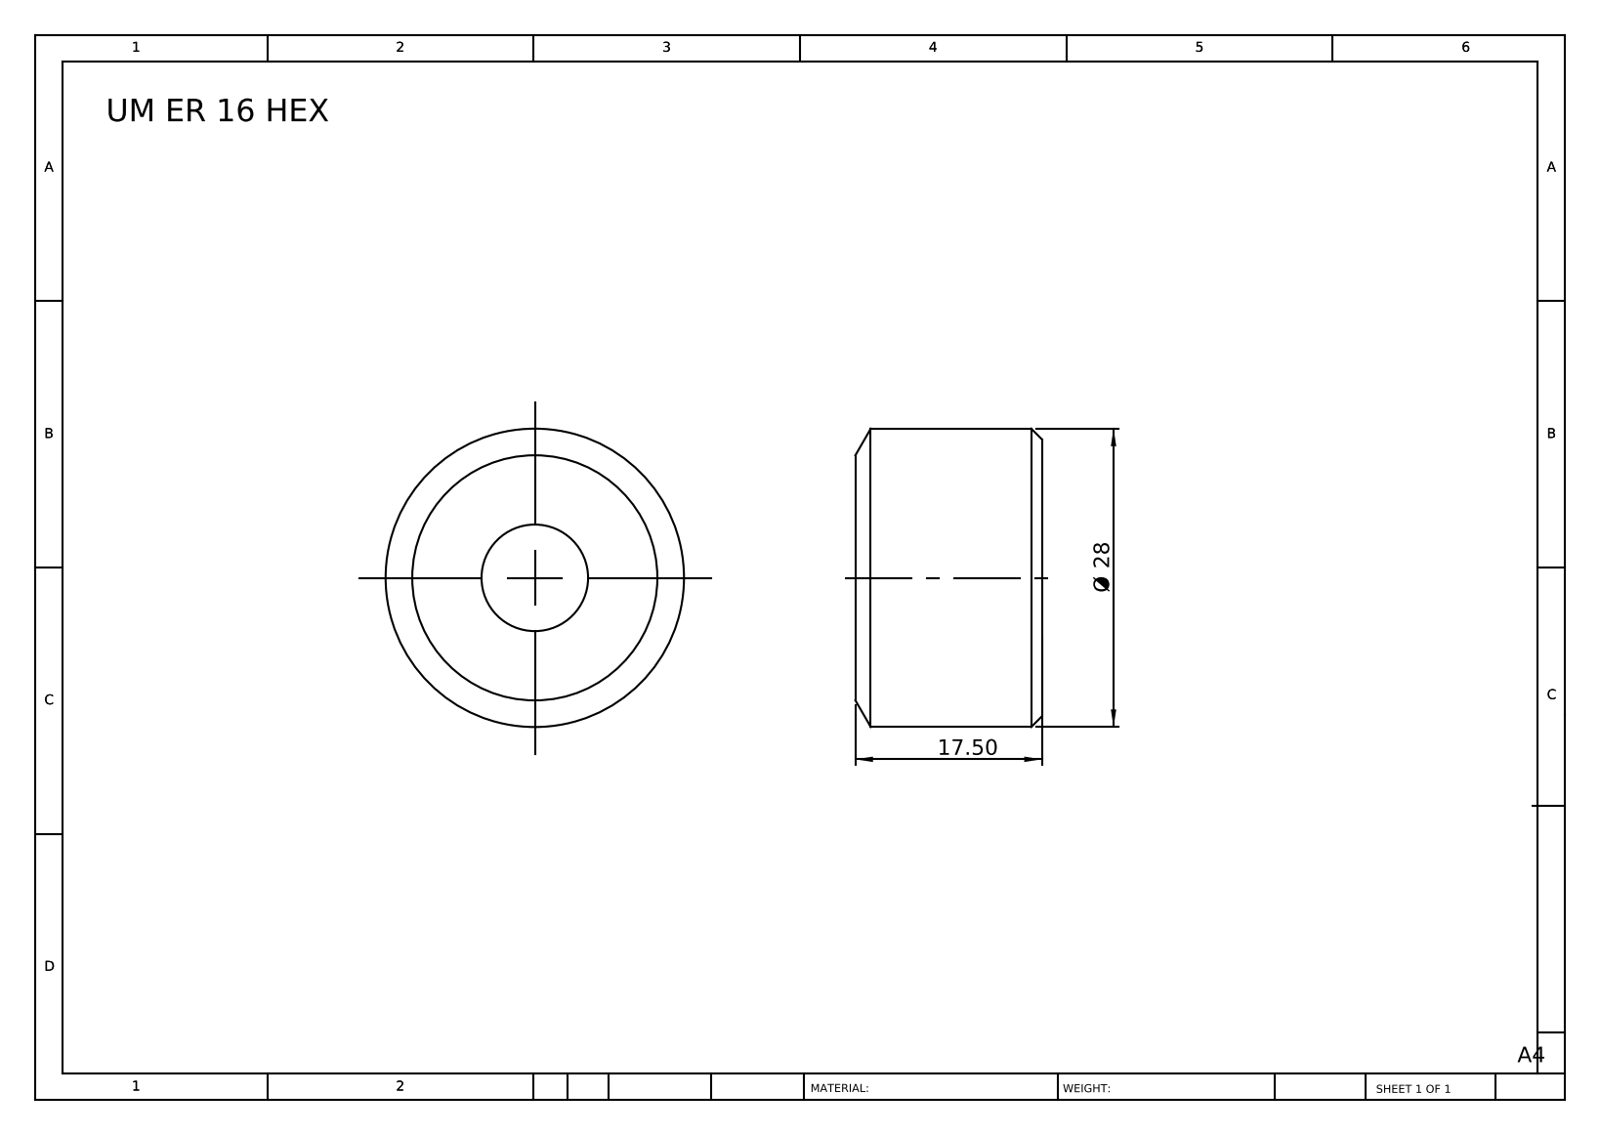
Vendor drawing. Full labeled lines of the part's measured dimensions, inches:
Part name (STEP PRODUCT): UM ER 16 HEX
STEP written by: SolidWorks 2014 (CONFIG_CONTROL_DESIGN)
Units: inches
Bodies: 1 solid, 10 faces (2 planar, 4 cylindrical, 4 other)
Overall size (bounding box): 1.102 × 1.102 × 0.689
Volume: 0.562 in³ · Surface area: 4.673 in²
Round holes (diameter × count): ⌀0.394 ×1
Round bosses / shafts (diameter × count): ⌀1.102 ×1
Main face-to-face distances: 0.689
